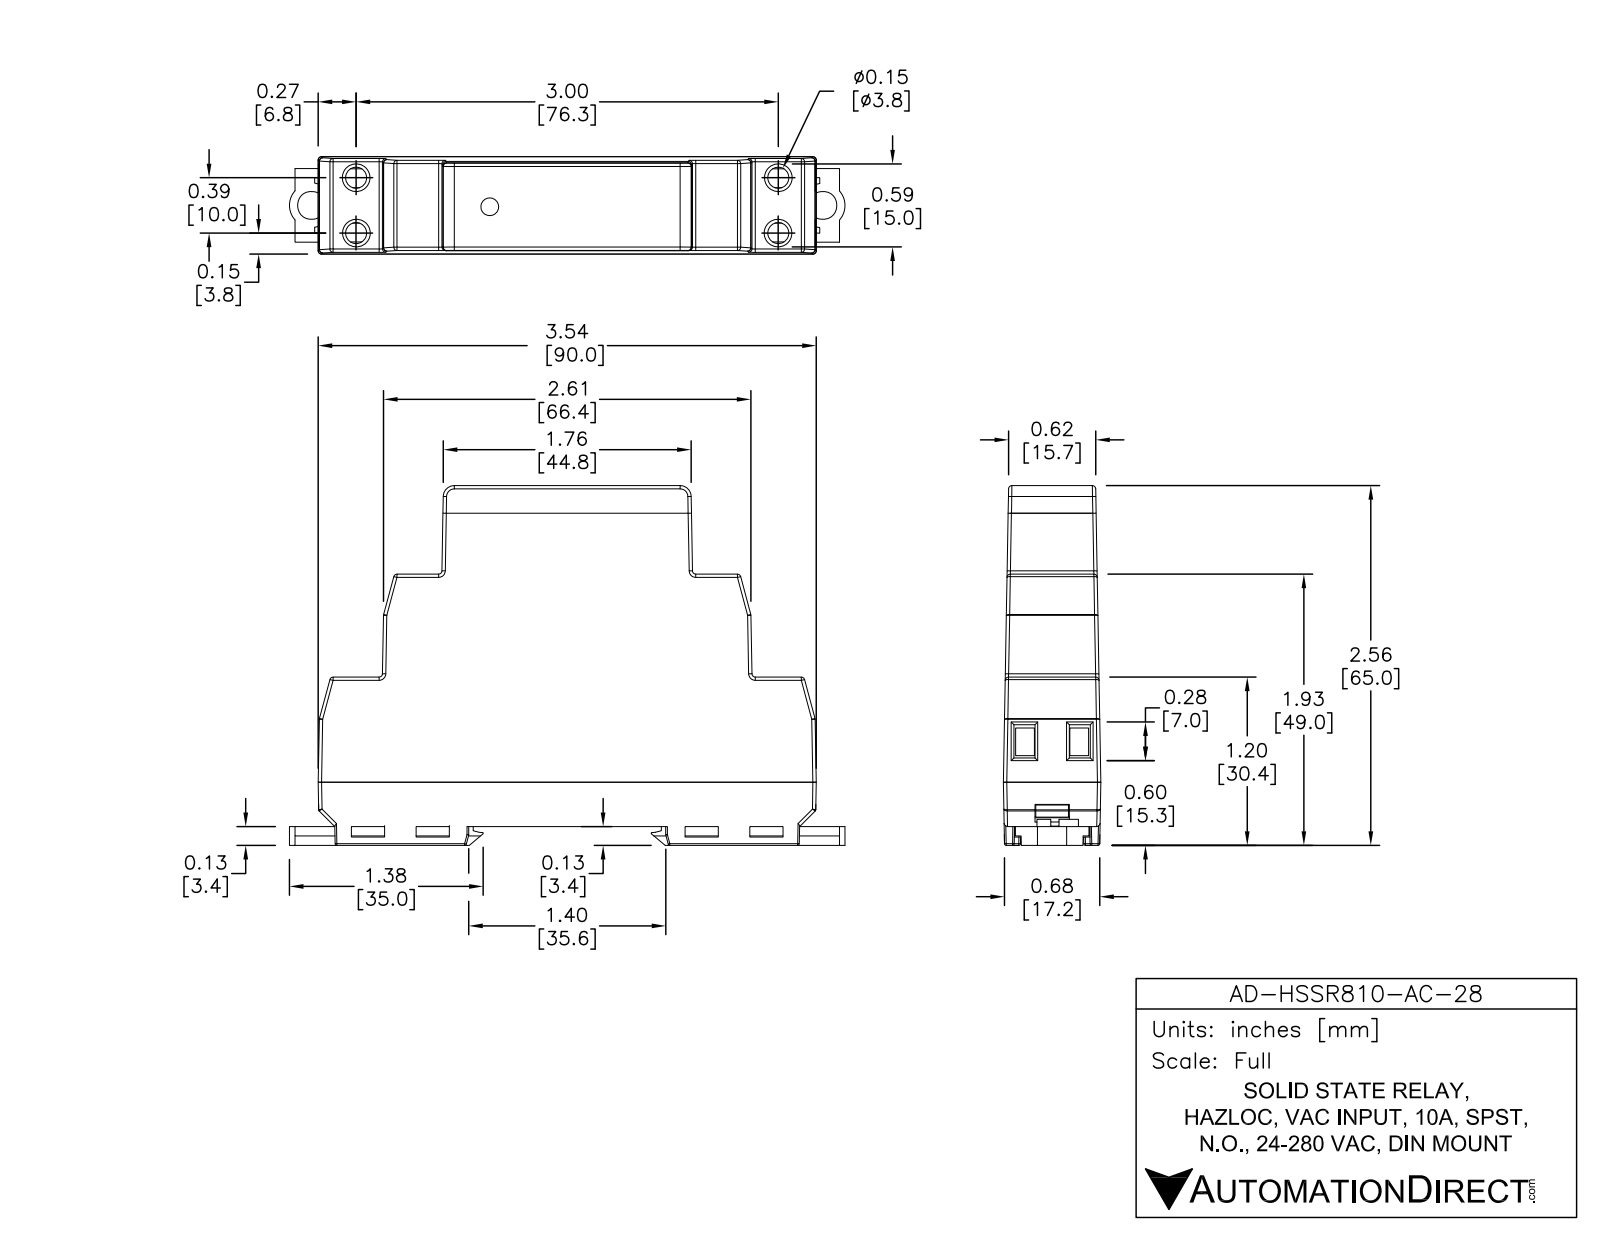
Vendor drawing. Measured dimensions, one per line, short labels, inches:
name: AD-HSSR810-AC-28
written by: SolidWorks 2013 (AUTOMOTIVE_DESIGN)
unit: in
bodies: 35 solids, 1268 faces (689 planar, 65 cylindrical, 514 other)
size: 3.952 × 2.619 × 0.692
volume: 4.725 in³; area: 25.56 in²
holes: 4× ⌀0.2, 2× ⌀0.19
bosses: 4× ⌀0.175, 1× ⌀0.1
rounds: 10× R0.02, 10× R0.024, 6× R0.012, 2× R0.079, 2× R0.15, 2× R45.93
face distances: 0.136, 2.559, 2.423, 0.134, 2.425, 1.929, 1.795, 1.793, 0.63, 1.197
hole spacings: 3.335, 0.379, 0.38, 0.4, 3.006, 3.033, 3.652
